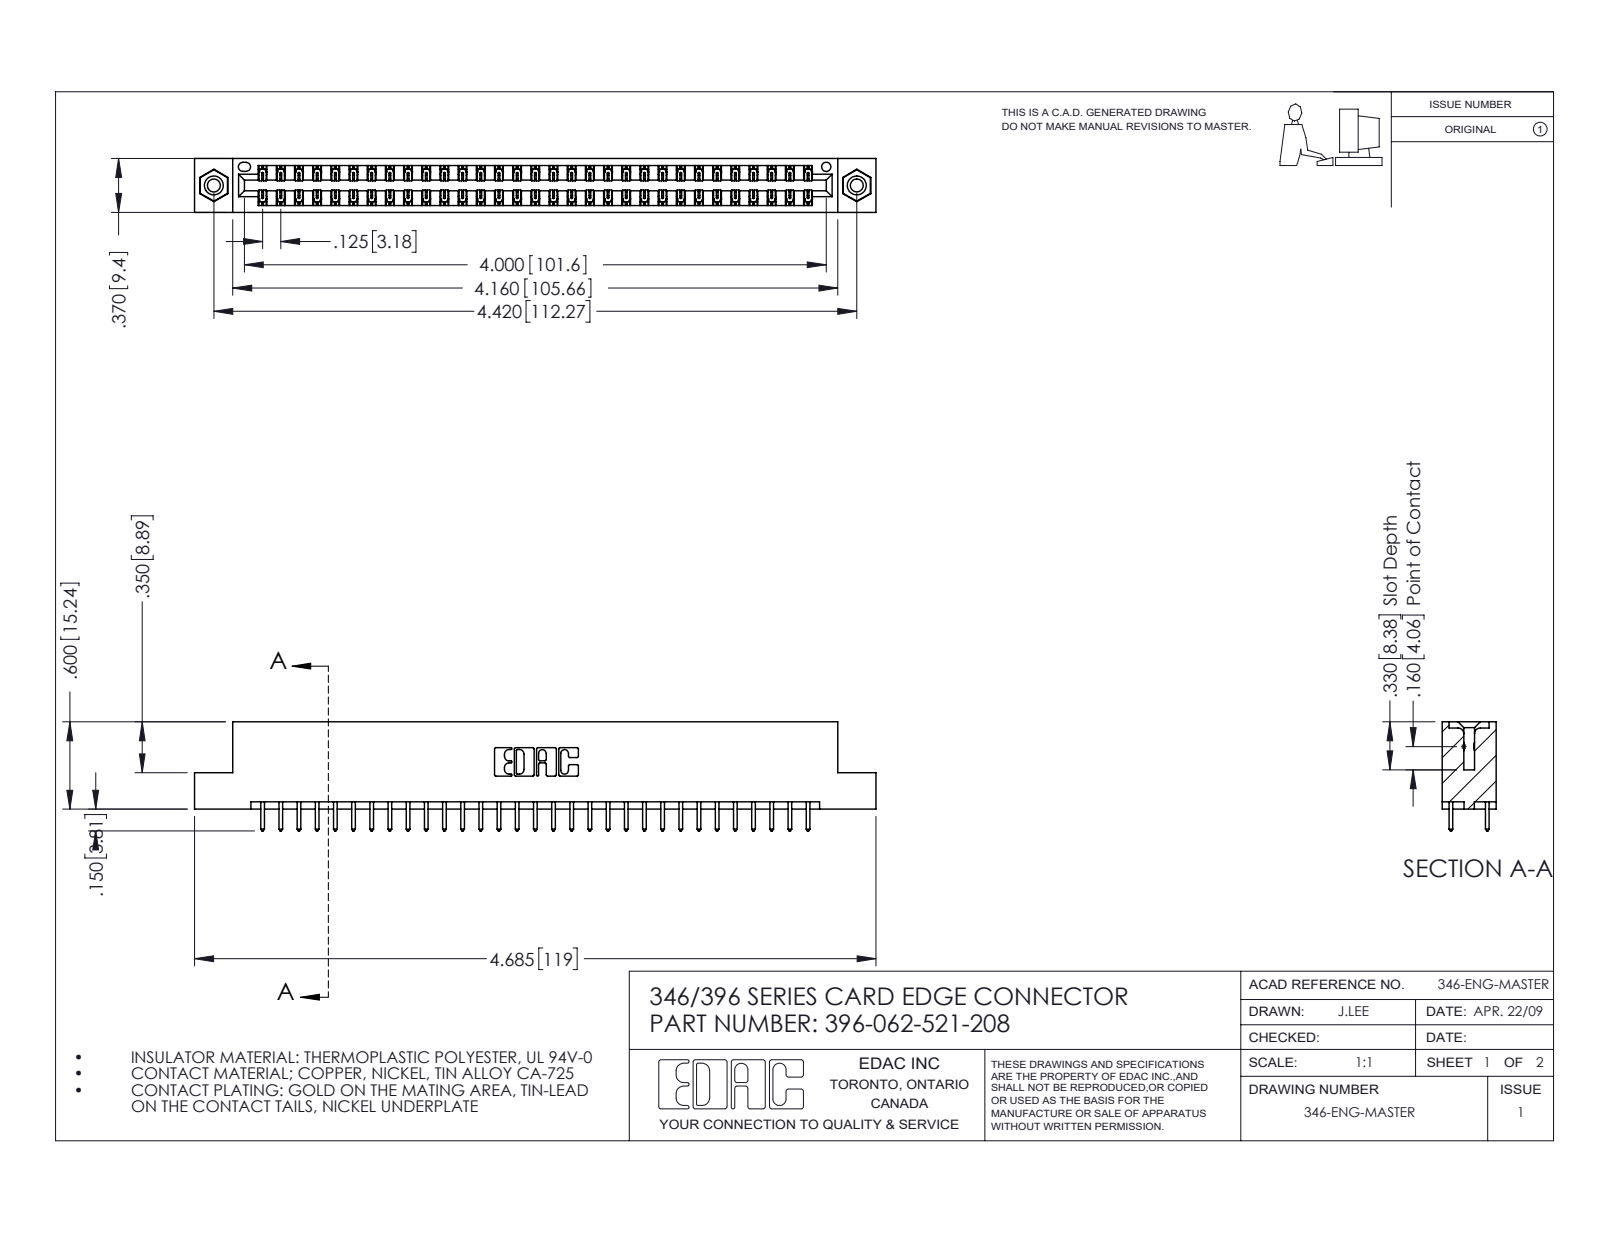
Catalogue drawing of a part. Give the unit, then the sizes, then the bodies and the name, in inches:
Units: inches
Overall size (bounding box): 4.685 × 0.75 × 0.37
Round holes (diameter × count): ⌀0.089 ×2, ⌀0.125 ×2, ⌀0.156 ×2, ⌀0.064 ×1
Round bosses / shafts (diameter × count): ⌀0.155 ×2
Partial cylindrical surfaces — rounded edges, fillets, slot ends (radius × count): R0.006 ×93, R0.01 ×62, R0.01 ×22, R0.007 ×6, R0.031 ×6, R0.026 ×3, R0.014 ×2, R0.022 ×2
Main face-to-face distances: 0.048, 0.322, 0.25, 0.37, 0.072, 0.298, 0.025, 0.275, 0.148, 0.222
Hole centre spacings: 0.246, 4.212, 4.42
Volume: 0.701 in³ · Surface area: 23.97 in²
Bodies: 65 solids, 3406 faces (2278 planar, 1112 cylindrical, 16 other)
Part name (STEP PRODUCT): 346 Part_Flush Mounting Lugs - 0.156 Dia-TI; 396-062-521-208; 345-250-001_345-250-003-102; 345-292-001_345-293-121
STEP written by: SolidWorks 2016 (CONFIG_CONTROL_DESIGN)
